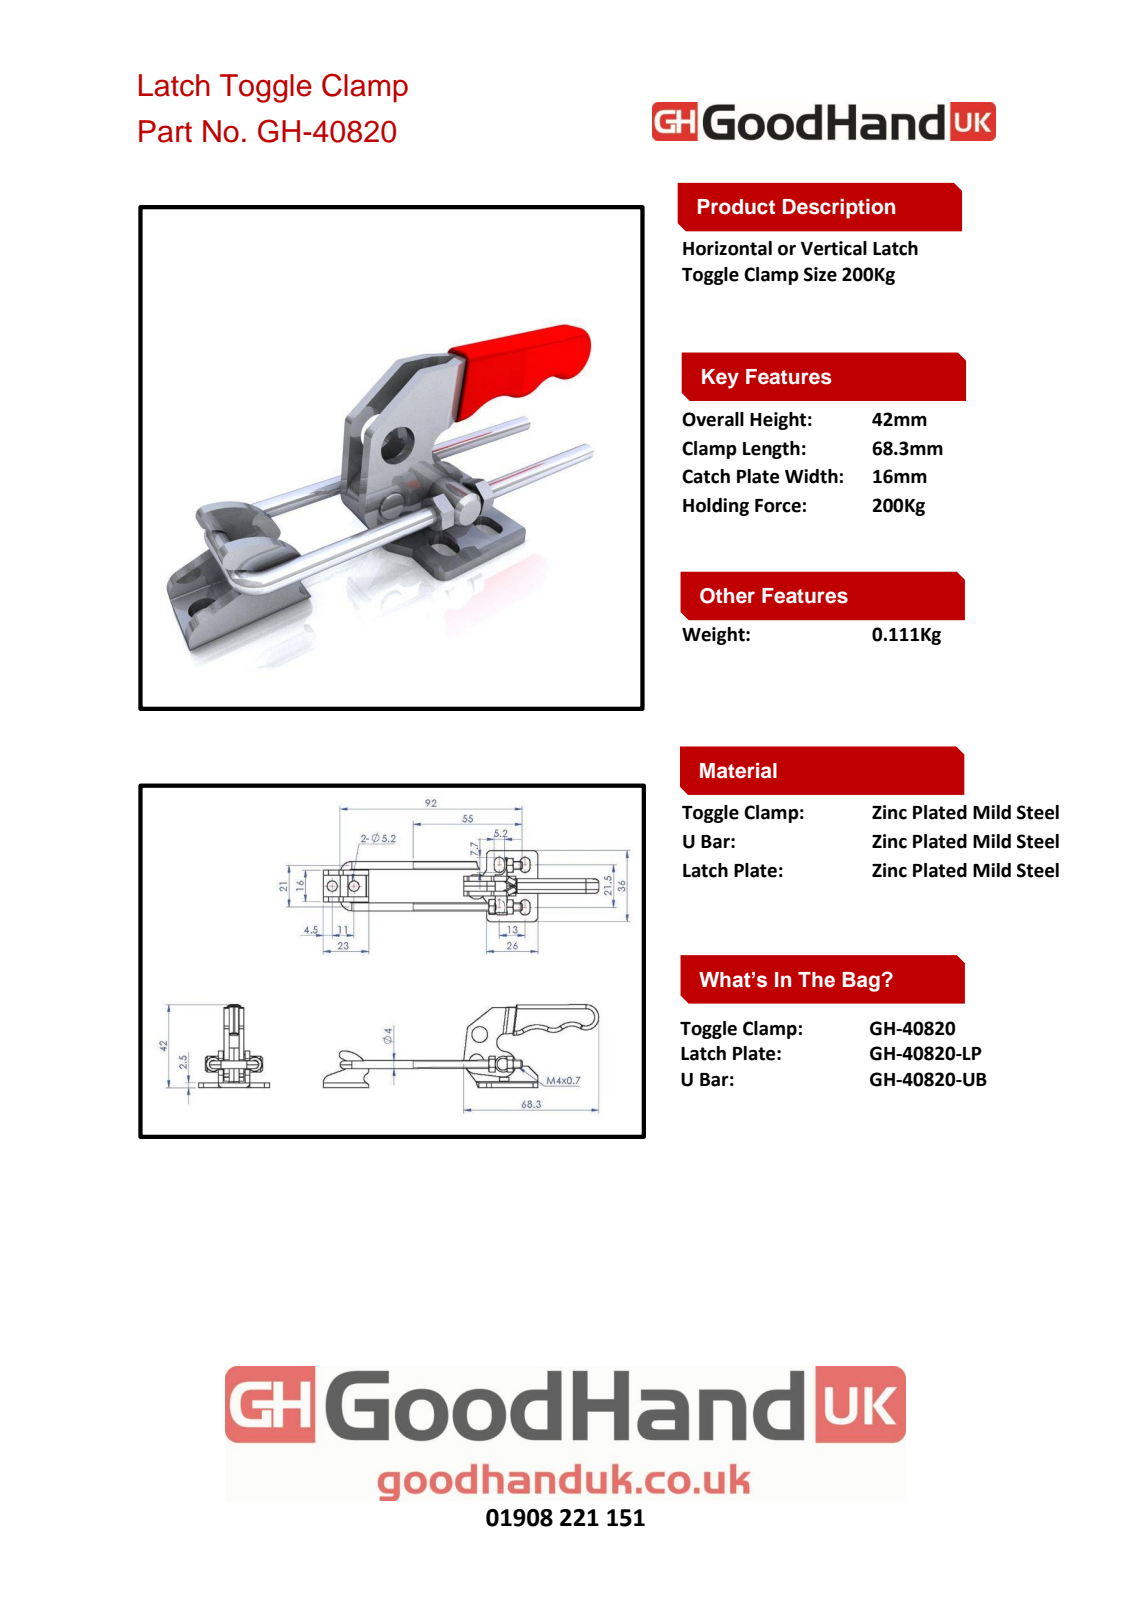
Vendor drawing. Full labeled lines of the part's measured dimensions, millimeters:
Part name (STEP PRODUCT): Group3^GH-40820(簡化); 44082044-1^GH-40820(簡化); GH-40820(簡化); Group2^GH-40820(簡化) (+2 more)
STEP written by: SolidWorks 2016 (AUTOMOTIVE_DESIGN)
Units: millimetres
Bodies: 7 solids, 287 faces (111 planar, 110 cylindrical, 66 other)
Overall size (bounding box): 139.25 × 42 × 36
Volume: 16 421 mm³ · Surface area: 13 890 mm²
Round holes (diameter × count): ⌀4 ×2, ⌀8 ×2, ⌀3 ×1
Round bosses / shafts (diameter × count): ⌀4 ×4
Partial cylindrical surfaces — rounded edges, fillets, slot ends (radius × count): R2 ×9, R2.5 ×9, R0.5 ×8, R2.6 ×8, R3 ×6, R4.5 ×4, R0.1 ×2, R6.5 ×2
Main face-to-face distances: 2.5, 7.5, 10.5, 5, 3, 10, 13, 0.5, 5.5, 13.5
Hole centre spacings: 13.49, 13.5, 19.09, 21
